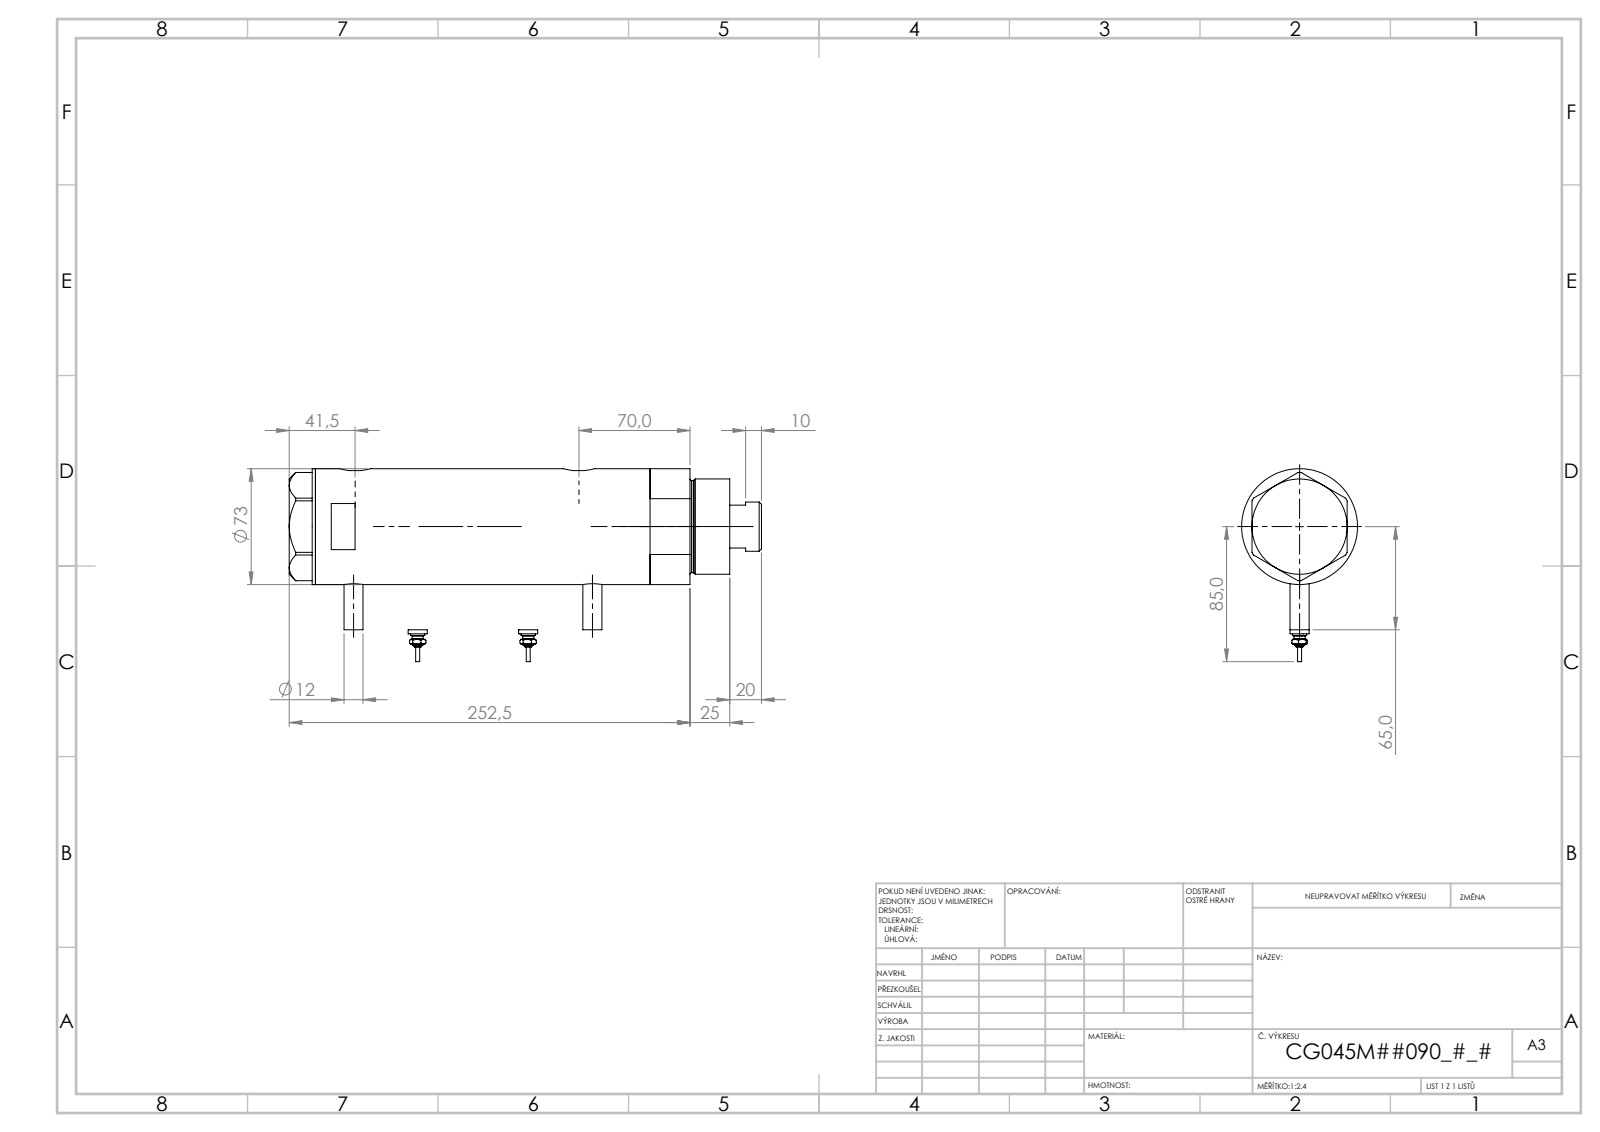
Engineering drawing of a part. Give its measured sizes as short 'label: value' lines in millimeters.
name: V270CG_FRONT; V270CG_SWITCH; V270CG_BACK; V270CG_VC (+1 more)
written by: SolidWorks 2019 (CONFIG_CONTROL_DESIGN)
unit: mm
bodies: 6 solids, 231 faces (78 planar, 79 cylindrical, 74 other)
size: 281.52 × 105.3 × 73
volume: 975 540 mm³; area: 164 299 mm²
holes: 2× ⌀5, 2× ⌀12.5, 2× ⌀13.16, 1× ⌀10.5, 1× ⌀32, 1× ⌀33.5, 1× ⌀45, 1× ⌀48, 1× ⌀64
bosses: 3× ⌀12, 2× ⌀9, 2× ⌀7, 2× ⌀4.34, 2× ⌀2.4, 1× ⌀73, 1× ⌀60, 1× ⌀58
rounds: 2× R10
face distances: 157.14, 26, 131.14, 16.5, 42.5, 173.64, 245.01, 261.51, 219.01, 87.87
hole spacings: 141.65, 0.99, 1, 8.5, 8.51, 132.15, 133.14, 133.15
